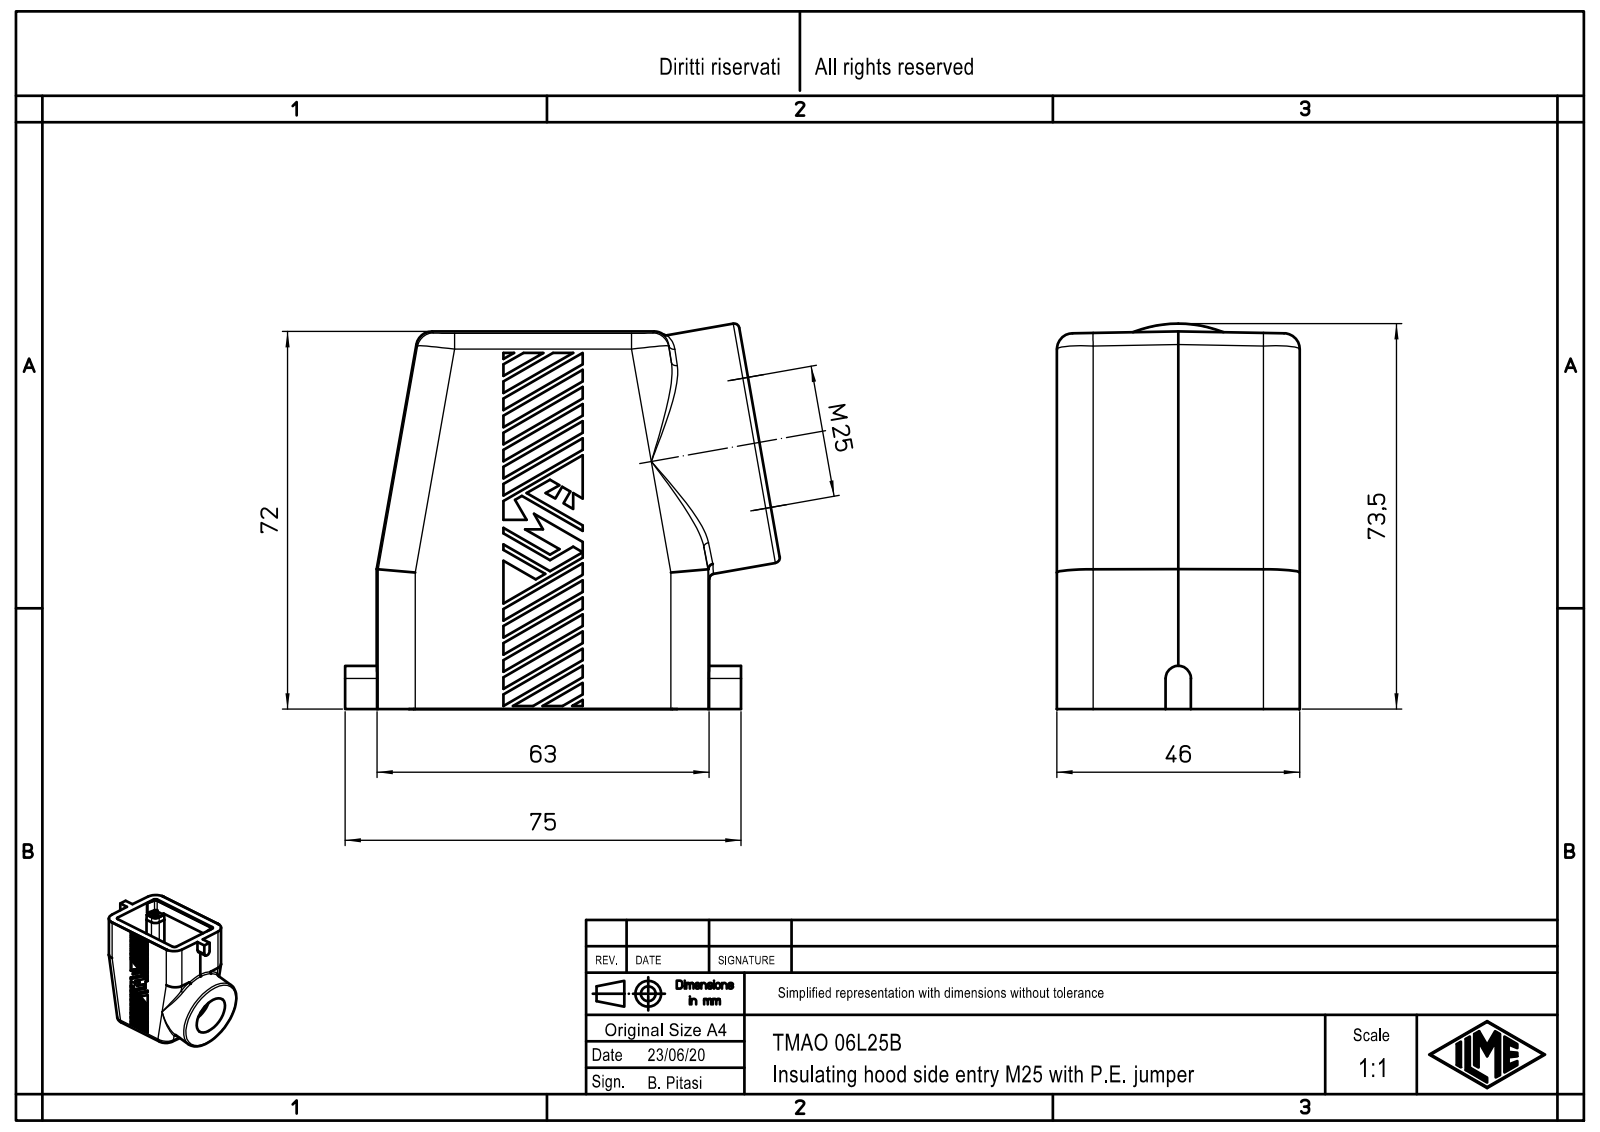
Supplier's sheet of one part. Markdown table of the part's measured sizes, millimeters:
| quantity | value |
| --- | --- |
| part name | TMAO_06L25B |
| STEP written by | Creo Elements/Direct Modeling 20.1B 02-Apr-2019 (C) Parametric Technology GmbH (AUTOMOTIVE_DESIGN) |
| units | millimeters |
| bodies | 1 solid, 567 faces (396 planar, 81 cylindrical, 90 other) |
| overall size | 82.33 × 72.99 × 46 |
| volume | 105 553 mm³ |
| surface area | 35 779 mm² |
| round holes (diameter × count) | 3 × 4, 3.5 × 4, 21 × 1, 25 × 1 |
| round bosses / shafts (diameter × count) | 4.8 × 4, 46 × 1 |
| partial cylindrical surfaces (radius × count) | 1.5 × 12, 7 × 8, 3 × 6, 1.3 × 4, 1.6 × 4, 2 × 4, 3.5 × 4, 2.4 × 1 |
| main face-to-face distances | 46, 0.5, 45.5, 66, 5.6, 26.52, 63, 6.1, 5.3, 45 |
| hole center spacings | 27, 44, 51.62 |
